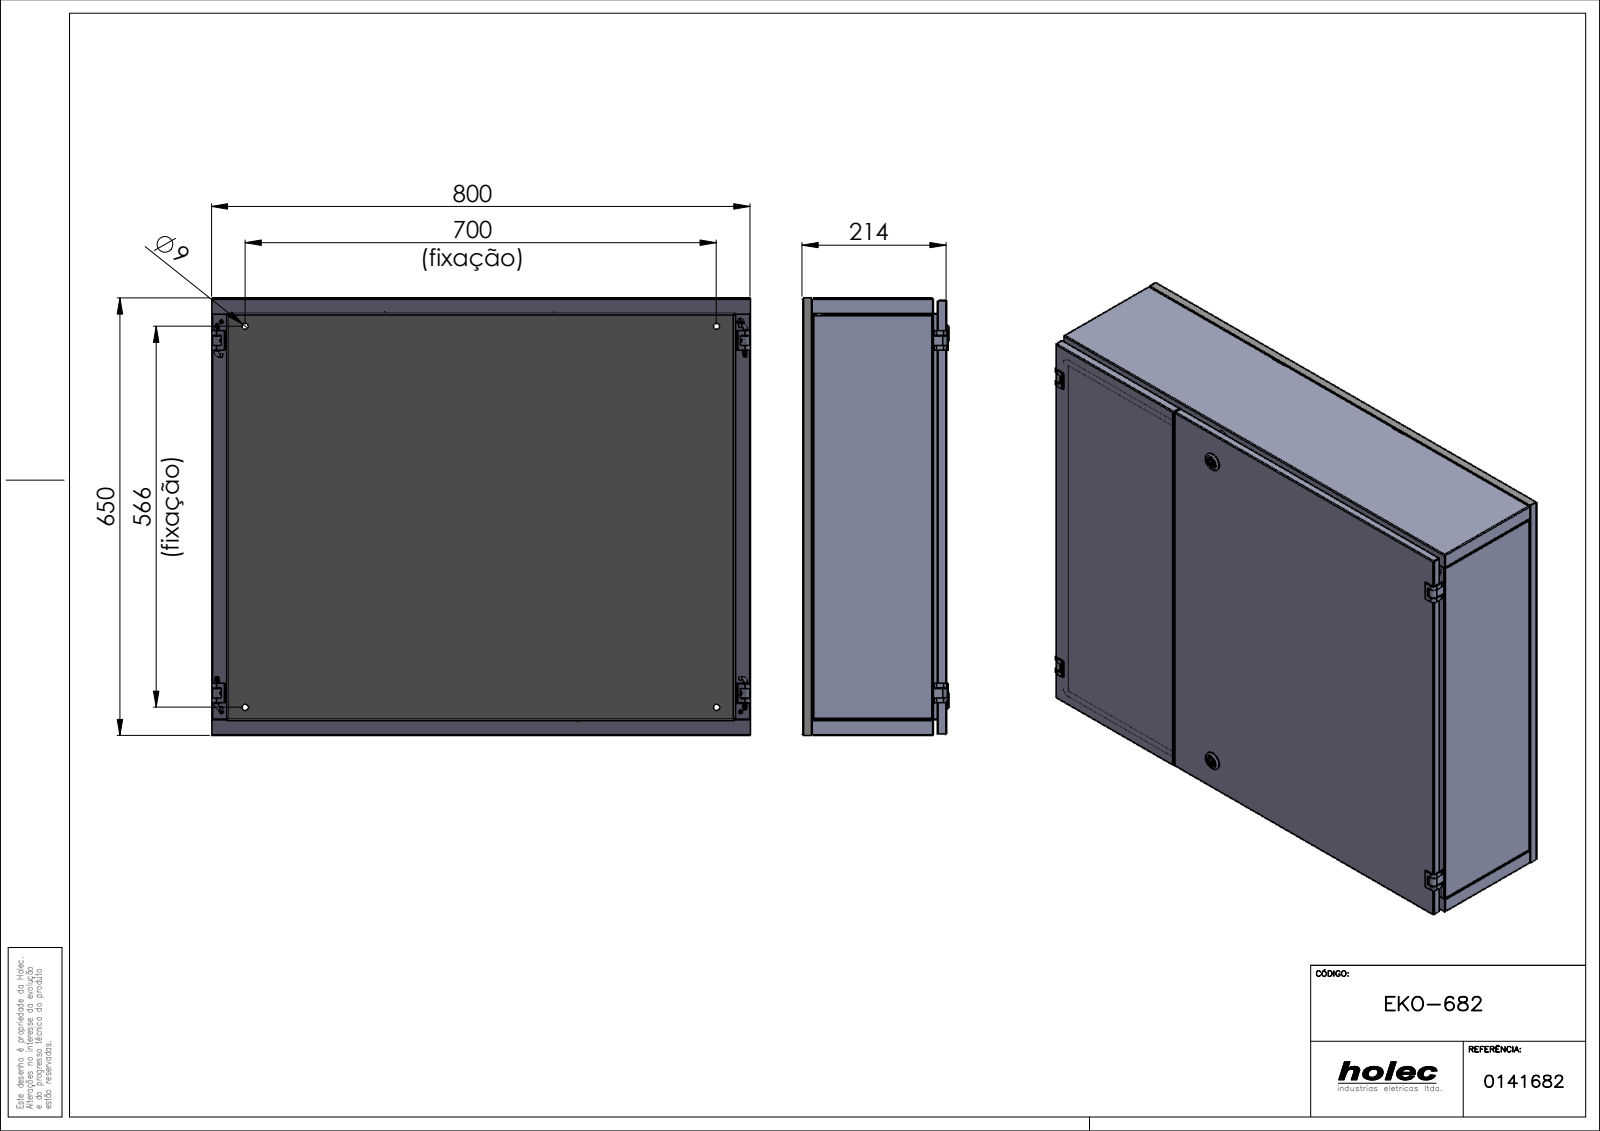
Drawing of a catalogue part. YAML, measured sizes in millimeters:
part_name: "EKO-682"
step_written_by: "SolidWorks 2017 (AUTOMOTIVE_DESIGN)"
units: millimeters
bodies: {solids: 53, faces: 3633, planar: 1785, cylindrical: 1142, other: 706}
overall_size: [800, 650, 218.1]
volume: 2169000
surface_area: 4194000
round_holes:
  - {diameter: 4.3, count: 36}
  - {diameter: 6, count: 14}
  - {diameter: 4.2, count: 12}
  - {diameter: 5.5, count: 8}
  - {diameter: 11, count: 8}
  - {diameter: 5, count: 6}
  - {diameter: 3.3, count: 4}
  - {diameter: 4, count: 4}
  - {diameter: 9, count: 4}
  - {diameter: 4.1, count: 2}
  - {diameter: 10, count: 2}
  - {diameter: 10.1, count: 2}
round_bosses_or_shafts:
  - {diameter: 4, count: 4}
  - {diameter: 28, count: 2}
  - {diameter: 19, count: 2}
  - {diameter: 15.7, count: 2}
  - {diameter: 15, count: 2}
  - {diameter: 12.7, count: 2}
  - {diameter: 9.5, count: 2}
  - {diameter: 5.85, count: 2}
partial_cylinders:
  - {radius: 0.2, count: 152}
  - {radius: 1.5, count: 59}
  - {radius: 0.5, count: 57}
  - {radius: 0.3, count: 40}
  - {radius: 1, count: 22}
  - {radius: 2.5, count: 14}
  - {radius: 2, count: 8}
  - {radius: 4.5, count: 6}
face_to_face_distances: [1, 213.1, 212.1, 214.1, 649, 799, 24, 650, 648, 22.9]
hole_center_spacings: [25, 31.4, 253.24, 252, 50, 53.49, 256.91, 19]
